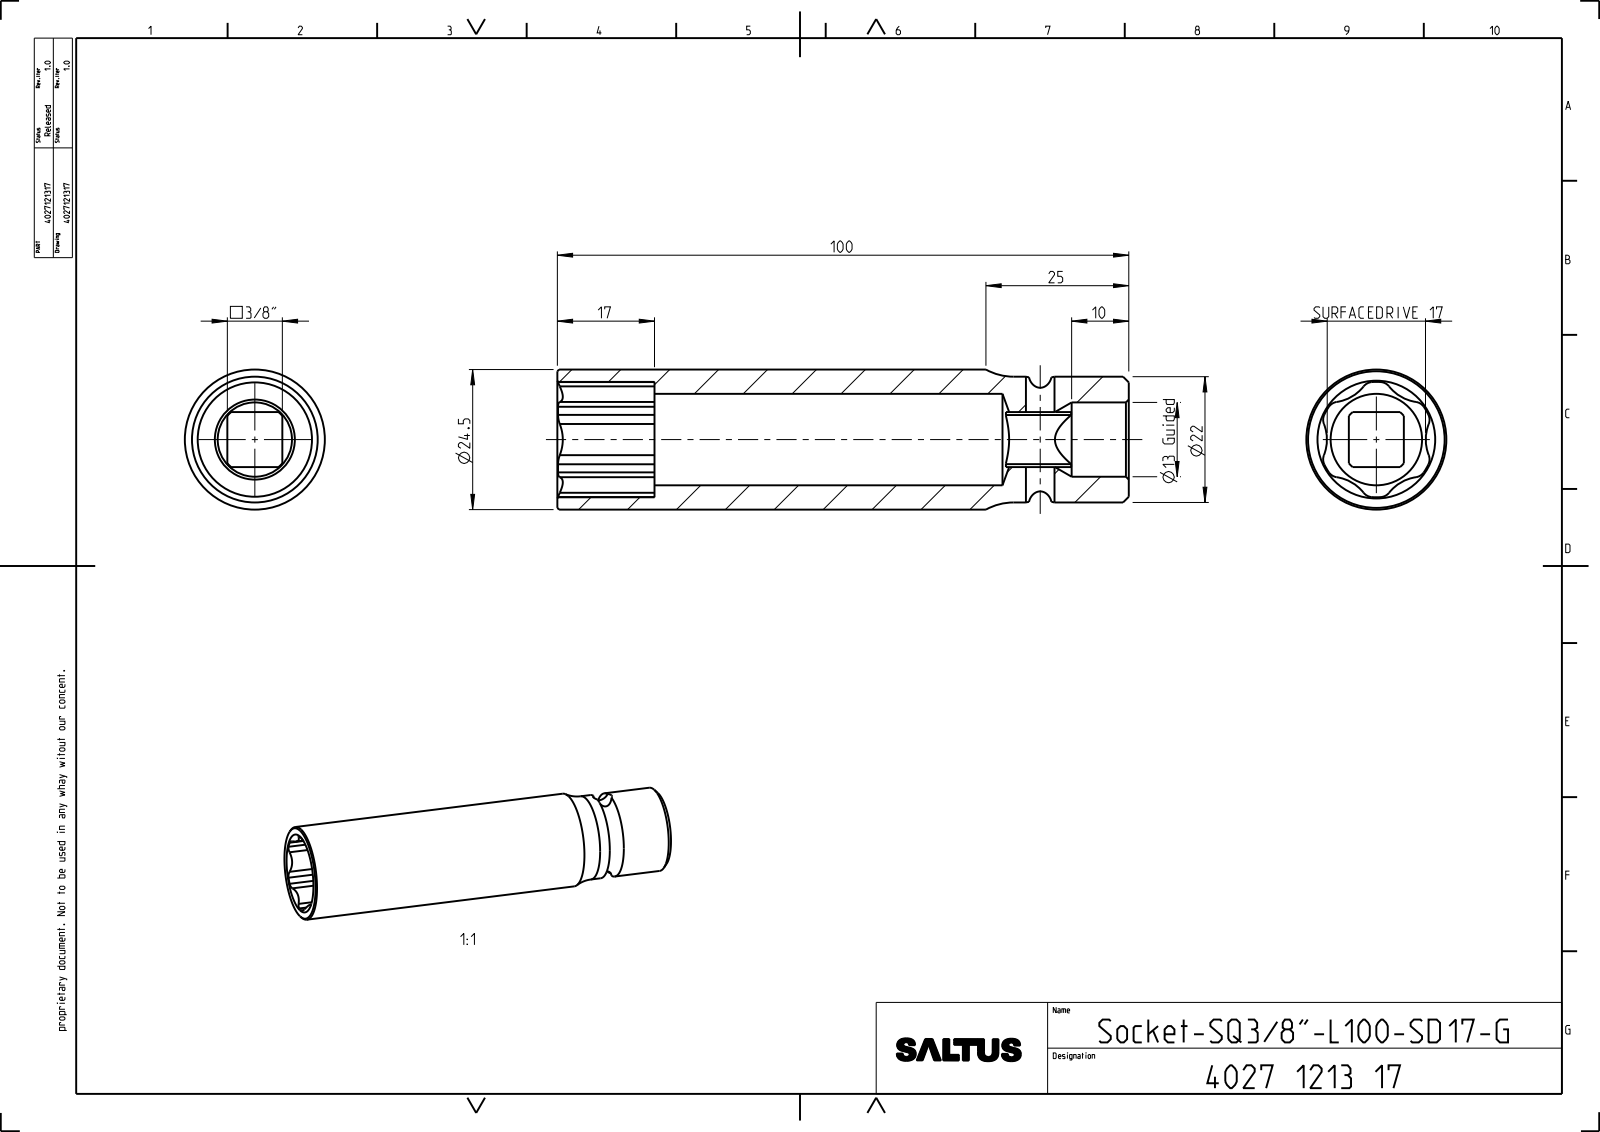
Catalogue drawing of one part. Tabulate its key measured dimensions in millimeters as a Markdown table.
| quantity | value |
| --- | --- |
| part name | 4027121317 |
| STEP written by | CREO PARAMETRIC BY PTC INC, 2022414 (CONFIG_CONTROL_DESIGN) |
| units | millimeters |
| bodies | 1 solid, 69 faces (11 planar, 42 cylindrical, 16 other) |
| overall size | 100 × 24.5 × 24.5 |
| volume | 24 916 mm³ |
| surface area | 13 196 mm² |
| round holes (diameter × count) | 5 × 1, 13 × 1, 16 × 1 |
| round bosses / shafts (diameter × count) | 24.5 × 1, 22 × 1 |
| partial cylindrical surfaces (radius × count) | 2 × 12, 7.4 × 6, 6.45 × 1, 10.09 × 1 |
| main face-to-face distances | 9.62, 100, 83, 17, 21.5, 61.5, 78.5 |
